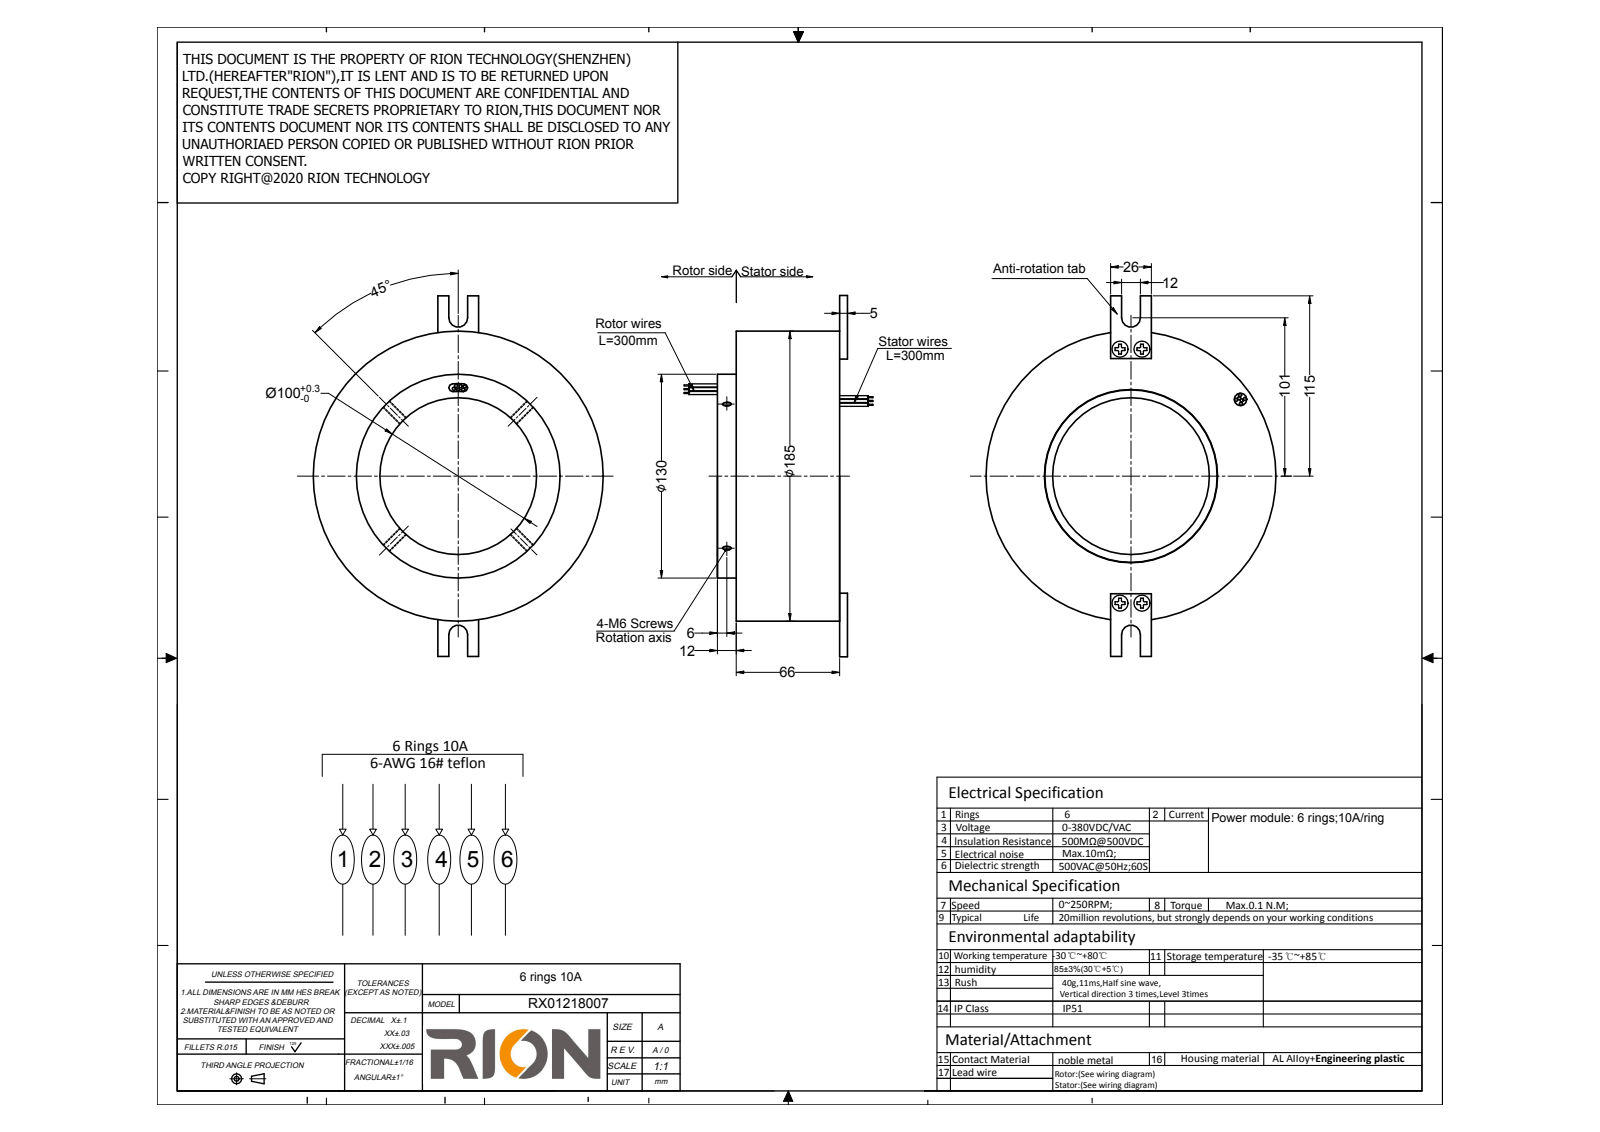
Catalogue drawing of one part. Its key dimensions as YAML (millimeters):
step_written_by: "SolidWorks 2014 (CONFIG_CONTROL_DESIGN)"
units: millimeters
bodies: {solids: 1, faces: 139, planar: 48, cylindrical: 75, other: 16}
overall_size: [230, 185, 155]
volume: 1327000
surface_area: 126308
round_holes:
  - {diameter: 5, count: 8}
  - {diameter: 4.2, count: 4}
  - {diameter: 8, count: 1}
  - {diameter: 100, count: 1}
  - {diameter: 110.5, count: 1}
  - {diameter: 177.2, count: 1}
round_bosses_or_shafts:
  - {diameter: 2.1, count: 12}
  - {diameter: 185, count: 1}
  - {diameter: 177, count: 1}
  - {diameter: 130, count: 1}
  - {diameter: 110.2, count: 1}
partial_cylinders:
  - {radius: 2.5, count: 2}
  - {radius: 6, count: 2}
  - {radius: 54, count: 1}
  - {radius: 59, count: 1}
face_to_face_distances: [66, 12, 78, 5, 83, 71, 26, 7, 19, 40]
hole_center_spacings: [81.3, 14, 162, 162.6, 75.72, 82.5, 87.95, 138.2]
